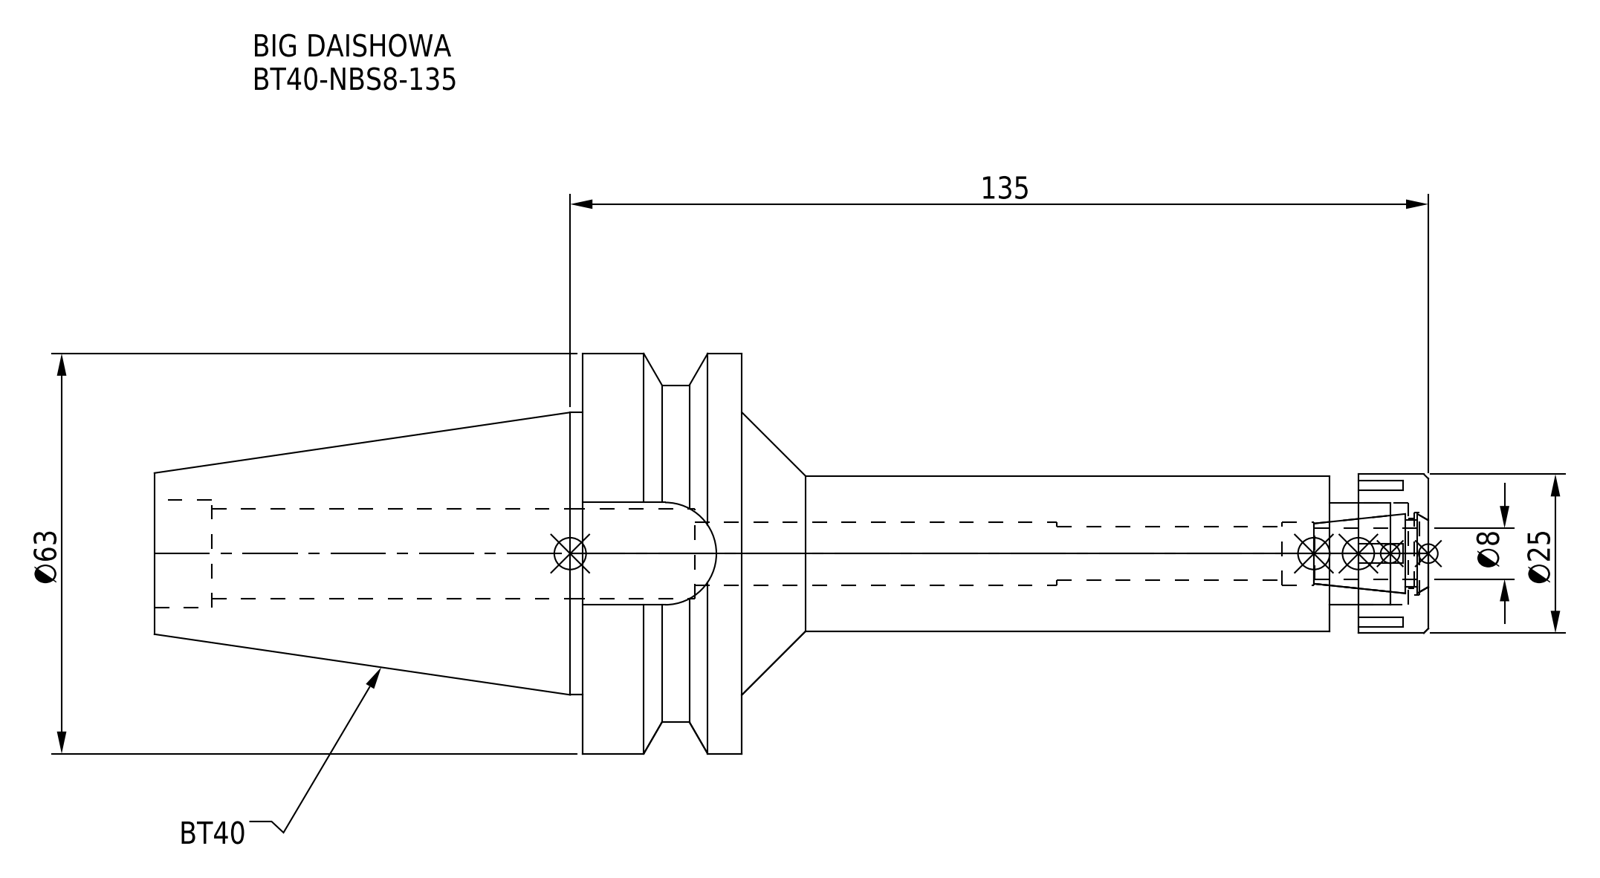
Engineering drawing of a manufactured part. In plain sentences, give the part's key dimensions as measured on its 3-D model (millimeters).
The part is named "BT40-NBS8-135.stp; BT40-NBS8-135; DXF_TEMP_ASSY_ASM_4_ASM.stp; BT40NB08135-080_ASM.stp (+3 more)". Its 3-D file was written by "SolidWorks 2019 (CONFIG_CONTROL_DESIGN)". It is 2 solids with 93 faces: 45 planar, 34 cylindrical and 14 other. Overall it measures 200.4 by 63 by 63 millimeters. Its volume is 165 989 cubic millimeters and its surface area 35 343 square millimeters. Round holes: 1 of diameter 8.4, 1 of diameter 10, 1 of diameter 11, 1 of diameter 13, 1 of diameter 14.2, 1 of diameter 16, 1 of diameter 17. Round bosses or shafts: 1 of diameter 63, 1 of diameter 53, 1 of diameter 44.45, 1 of diameter 25, 1 of diameter 24.5. Partial cylindrical surfaces (rounded edges, fillets, slot ends): 1 of radius 8.05. The main face-to-face distances are 25, 133, 108, 45, 92.4, 200.4, 67.4, 15.5, 92.5, 117.5.
